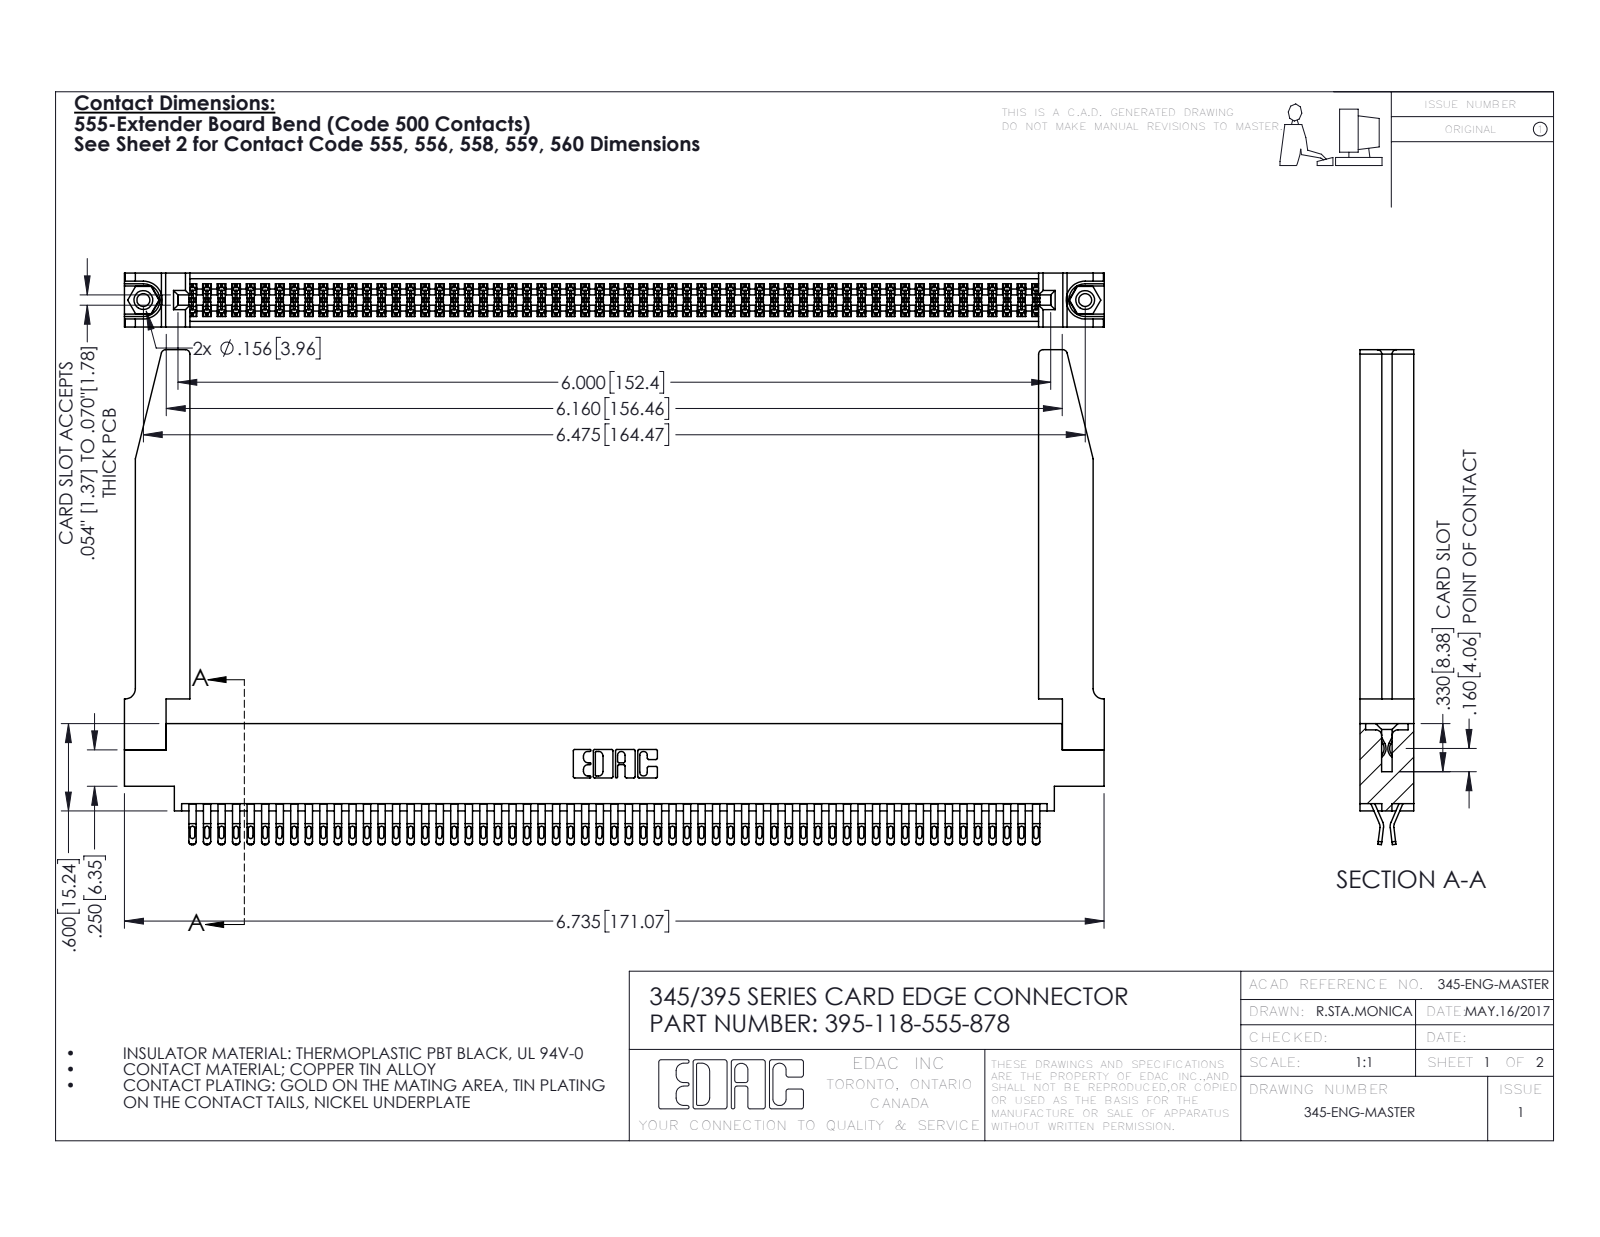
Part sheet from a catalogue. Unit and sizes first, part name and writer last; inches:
Units: inches
Overall size (bounding box): 6.736 × 3.402 × 0.37
Round holes (diameter × count): ⌀0.089 ×2, ⌀0.125 ×2, ⌀0.156 ×2, ⌀0.064 ×1
Round bosses / shafts (diameter × count): ⌀0.155 ×2
Partial cylindrical surfaces — rounded edges, fillets, slot ends (radius × count): R0.016 ×295, R0.02 ×236, R0.006 ×177, R0.01 ×22, R0.03 ×8, R0.007 ×6, R0.031 ×6, R0.026 ×3
Main face-to-face distances: 0.072, 0.37, 0.298, 0.025, 0.098, 0.272, 0.2, 0.225, 0.175, 0.148
Hole centre spacings: 0.27, 6.239, 6.475
Volume: 1.512 in³ · Surface area: 52.14 in²
Bodies: 123 solids, 6972 faces (3884 planar, 3036 cylindrical, 52 other)
Part name (STEP PRODUCT): 345-250-001_345-250-001-102; 345-292-001_555 Tail; 395-118-555-878; 345 Part_0.170 Offset - 0.156 Dia-TH (+1 more)
STEP written by: SolidWorks 2016 (CONFIG_CONTROL_DESIGN)
